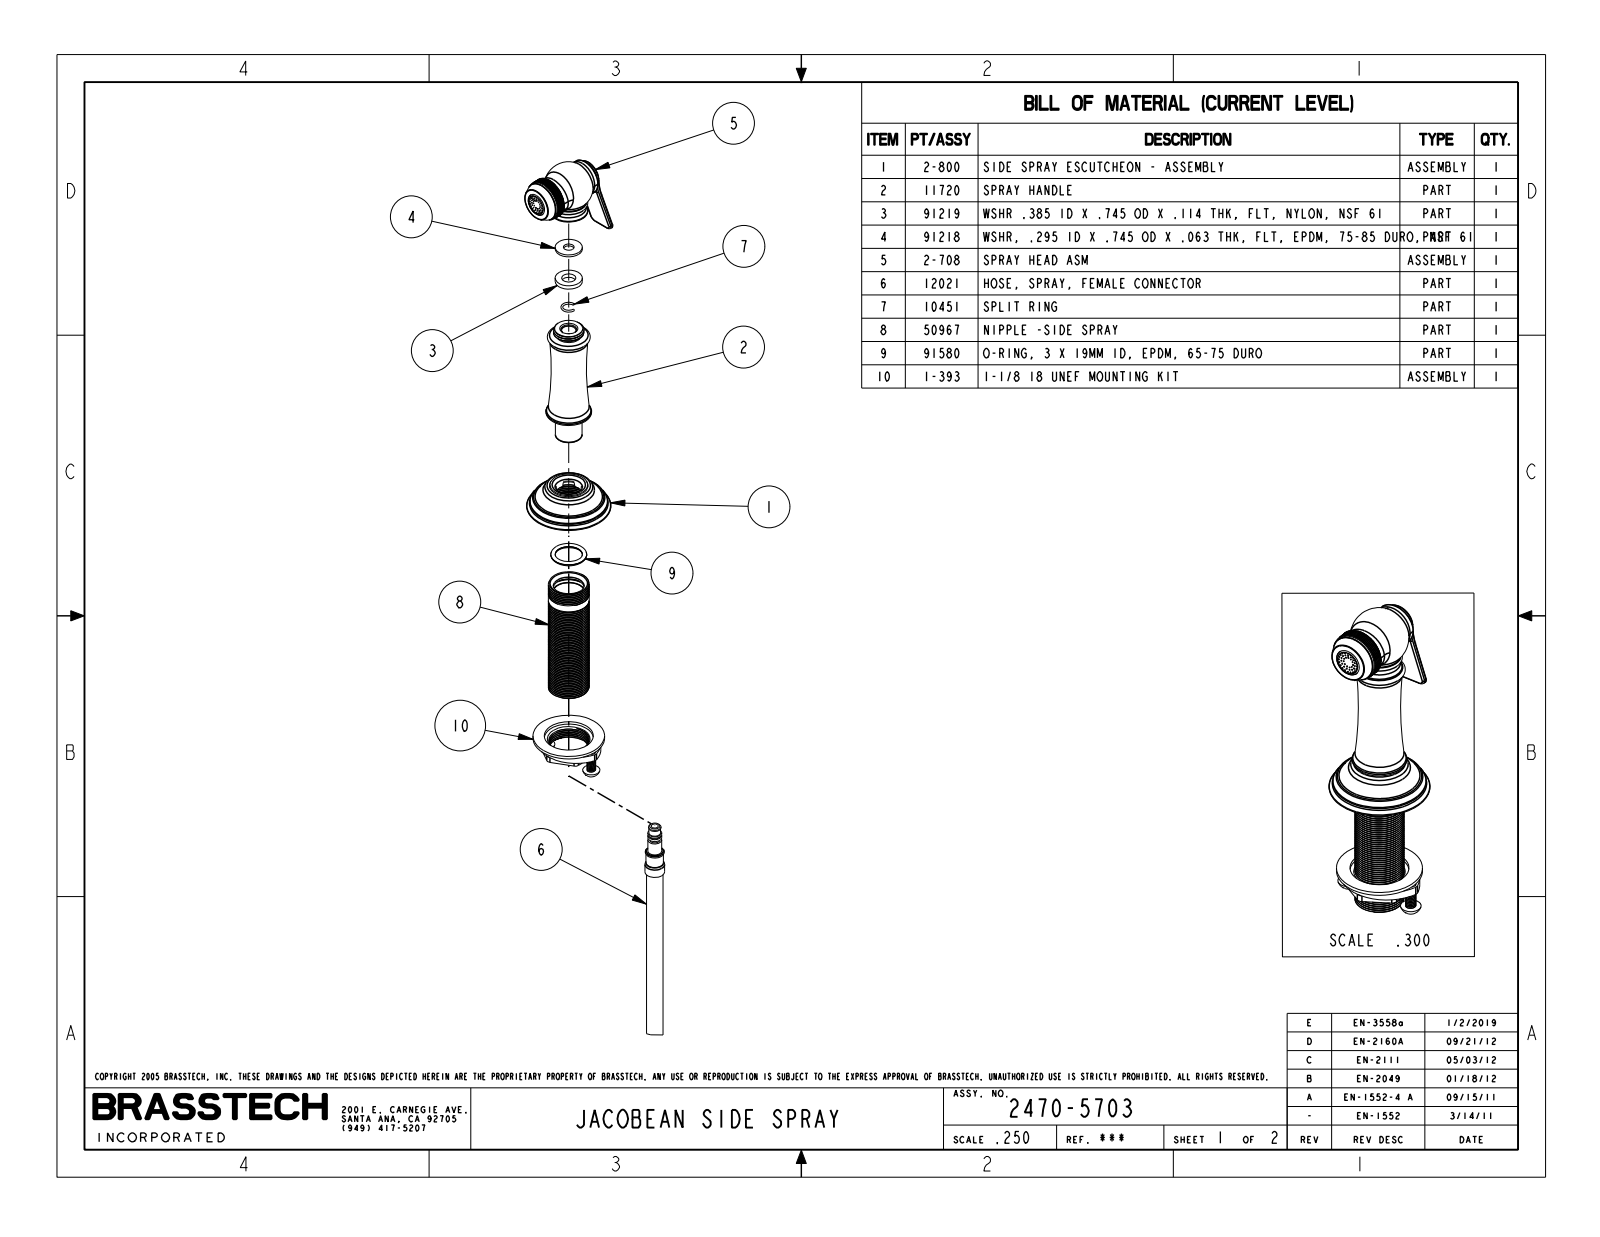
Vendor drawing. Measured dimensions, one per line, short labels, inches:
name: 11719; 91543; 2-800_ASM; 11720 (+8 more)
written by: PRO/ENGINEER BY PARAMETRIC TECHNOLOGY CORPORATION, 2009300 (CONFIG_CONTROL_DESIGN)
unit: in
bodies: 19 solids, 1125 faces (374 planar, 451 cylindrical, 300 other)
size: 4.897 × 2.663 × 2.319
volume: 4.771 in³; area: 73.7 in²
holes: 46× ⌀0.026, 2× ⌀0.875, 1× ⌀0.06, 1× ⌀0.13, 1× ⌀0.18, 1× ⌀0.215, 1× ⌀0.235, 1× ⌀0.24, 1× ⌀0.242, 1× ⌀0.368, 1× ⌀0.391, 1× ⌀0.438
bosses: 1× ⌀1.749, 1× ⌀1.1, 1× ⌀0.948, 1× ⌀0.862, 1× ⌀0.85, 1× ⌀0.84, 1× ⌀0.833, 1× ⌀0.821
rounds: 10× R0.04, 8× R0.03, 4× R0.01, 2× R0.08, 2× R0.156, 2× R0.16, 1× R0.06, 1× R0.219
face distances: 0.05, 0.131, 0.731, 3.356, 3.306, 0.165, 0.08, 0.03, 3.276, 0.681
hole spacings: 0.25, 0.494, 0.154, 0.476, 0.354, 0.078, 0.404, 0.294
